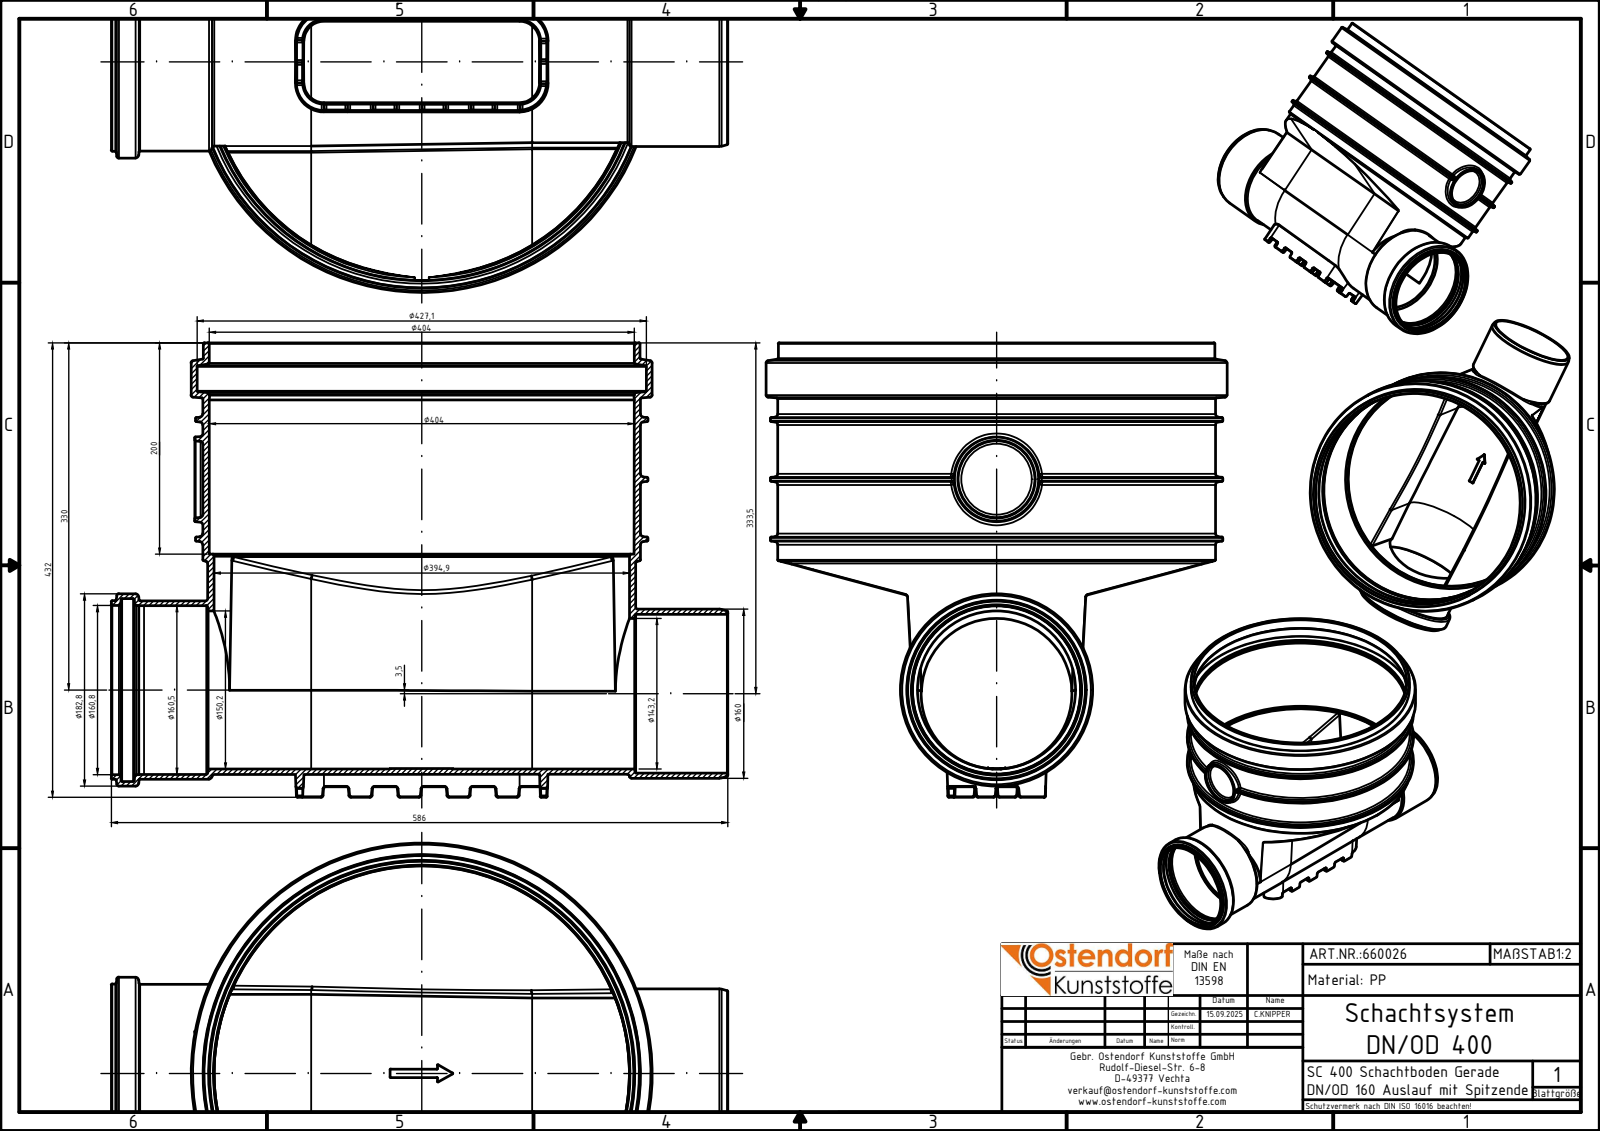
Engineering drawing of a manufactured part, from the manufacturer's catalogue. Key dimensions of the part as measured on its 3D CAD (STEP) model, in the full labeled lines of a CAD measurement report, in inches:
Part name (STEP PRODUCT): 660026 SC Schachtboden Typ G DN_OD 400_160 mit Spitzende
STEP written by: Autodesk Inventor 2024 (AUTOMOTIVE_DESIGN)
Units: inches
Bodies: 1 solid, 566 faces (88 planar, 173 cylindrical, 305 other)
Overall size (bounding box): 23.071 × 17.248 × 17.008
Volume: 271.2 in³ · Surface area: 2 186 in²
Round holes (diameter × count): ⌀5.638 ×1, ⌀5.913 ×1, ⌀5.941 ×1, ⌀6.319 ×1, ⌀6.331 ×1, ⌀6.843 ×1, ⌀15.547 ×1, ⌀15.906 ×1, ⌀16.815 ×1
Round bosses / shafts (diameter × count): ⌀17.248 ×1, ⌀16.929 ×1, ⌀16.378 ×1, ⌀16.339 ×1, ⌀16.02 ×1, ⌀7.197 ×1, ⌀6.685 ×1, ⌀6.673 ×1
Partial cylindrical surfaces — rounded edges, fillets, slot ends (radius × count): R0.039 ×56, R0.079 ×54, R0.02 ×7, R3.016 ×1, R3.147 ×1, R3.149 ×1
Main face-to-face distances: 0.13, 3.382, 7.909, 8.706, 16.614, 3.425, 0.394, 9.099, 17.008, 9.124
Hole centre spacings: 0.138
